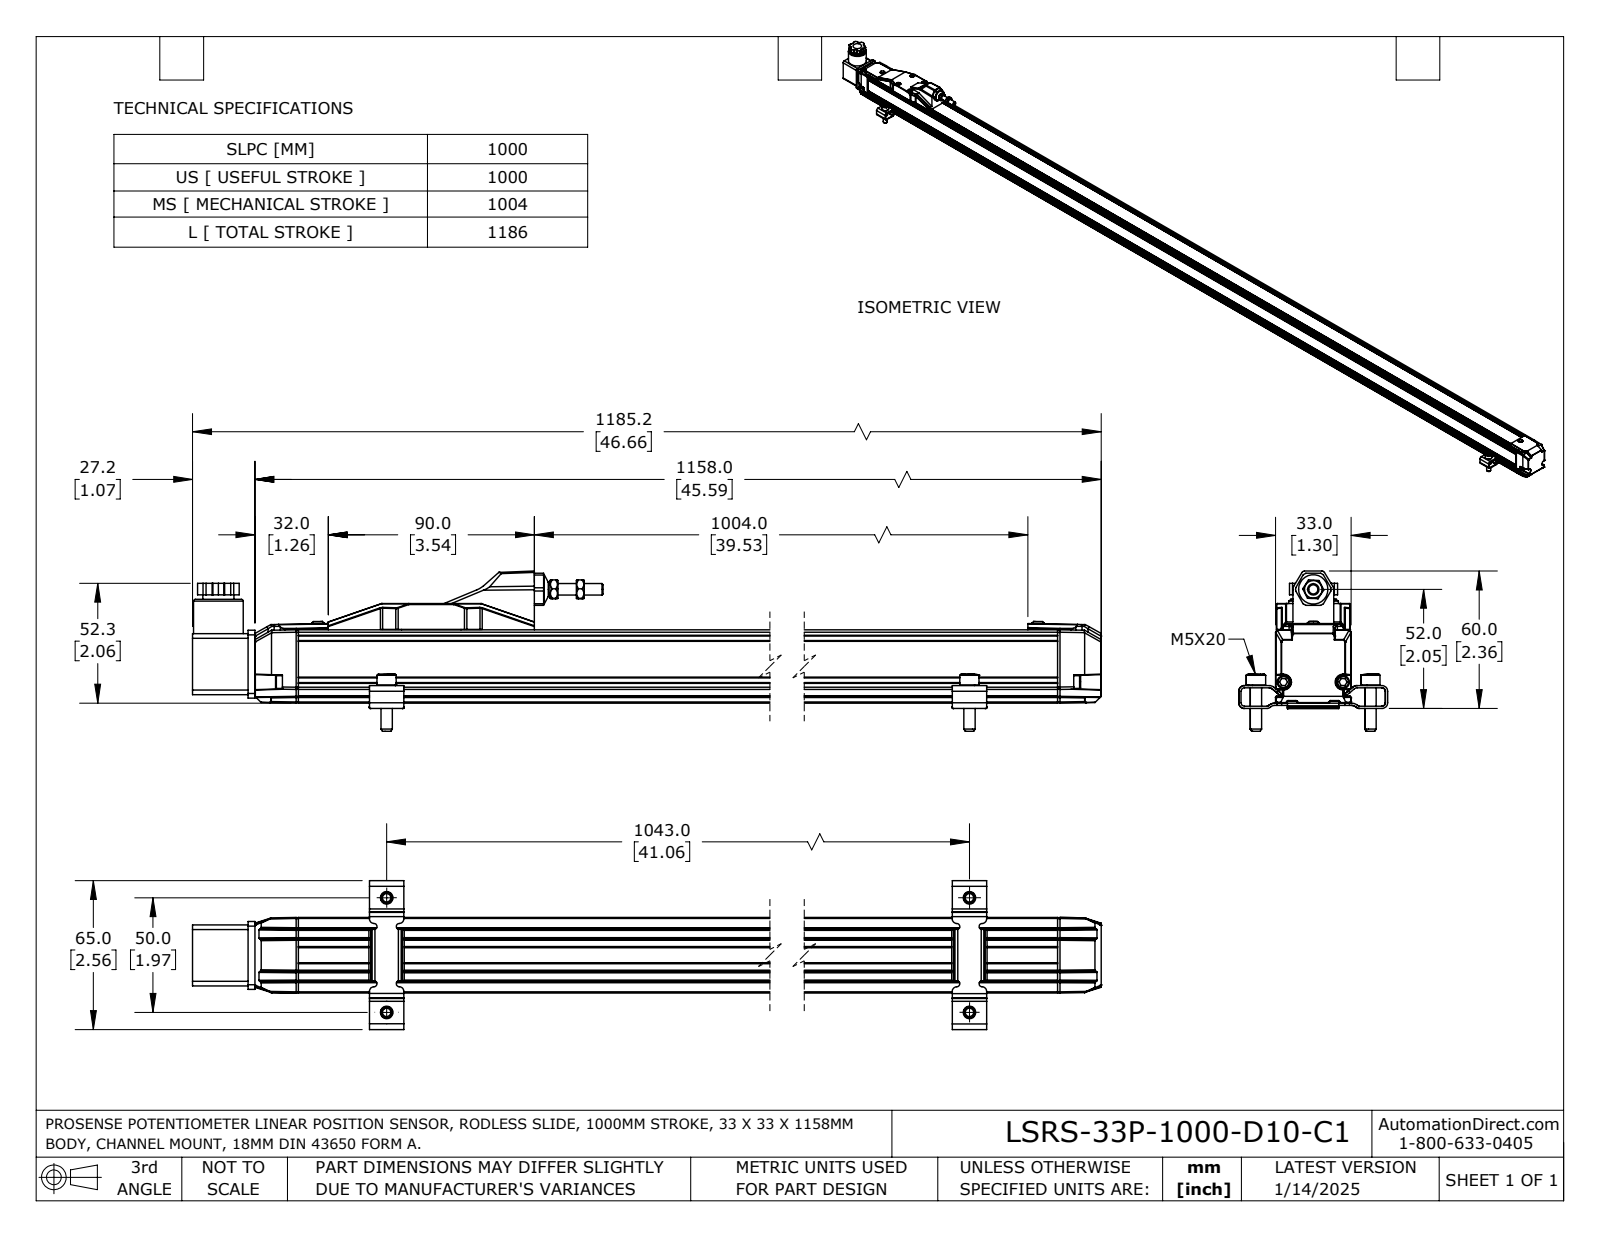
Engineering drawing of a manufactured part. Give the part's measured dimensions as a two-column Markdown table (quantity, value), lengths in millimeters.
| quantity | value |
| --- | --- |
| part name | LSRS-33P-1000-D10-C1 |
| STEP written by | SolidWorks 2024 (AUTOMOTIVE_DESIGN) |
| units | millimeters |
| bodies | 10 solids, 1310 faces (821 planar, 357 cylindrical, 132 other) |
| overall size | 1185.2 × 70 × 65 |
| volume | 1 122 000 mm³ |
| surface area | 253 000 mm² |
| round holes (diameter × count) | 4.7 × 4, 5.5 × 4, 2.7 × 2, 3.3 × 2, 4 × 1, 5 × 1, 5.3 × 1, 5.9 × 1, 6 × 1, 7 × 1, 10 × 1, 10.5 × 1 |
| round bosses / shafts (diameter × count) | 8.4 × 4, 4.9 × 4, 4.6 × 4, 5.6 × 2, 5.5 × 2, 3 × 2, 2.9 × 2, 2.9 × 2 |
| partial cylindrical surfaces (radius × count) | 0.5 × 78, 0.2 × 62, 2 × 44, 3 × 26, 1 × 10, 1.3 × 8, 1.5 × 8, 4 × 8 |
| main face-to-face distances | 33, 3, 31.6, 29.6, 6, 25.6, 0.9, 0.4, 32.6, 11.3 |
| hole center spacings | 15.2, 20, 23.7, 31, 32.7, 42.5, 50, 1014.2 |
